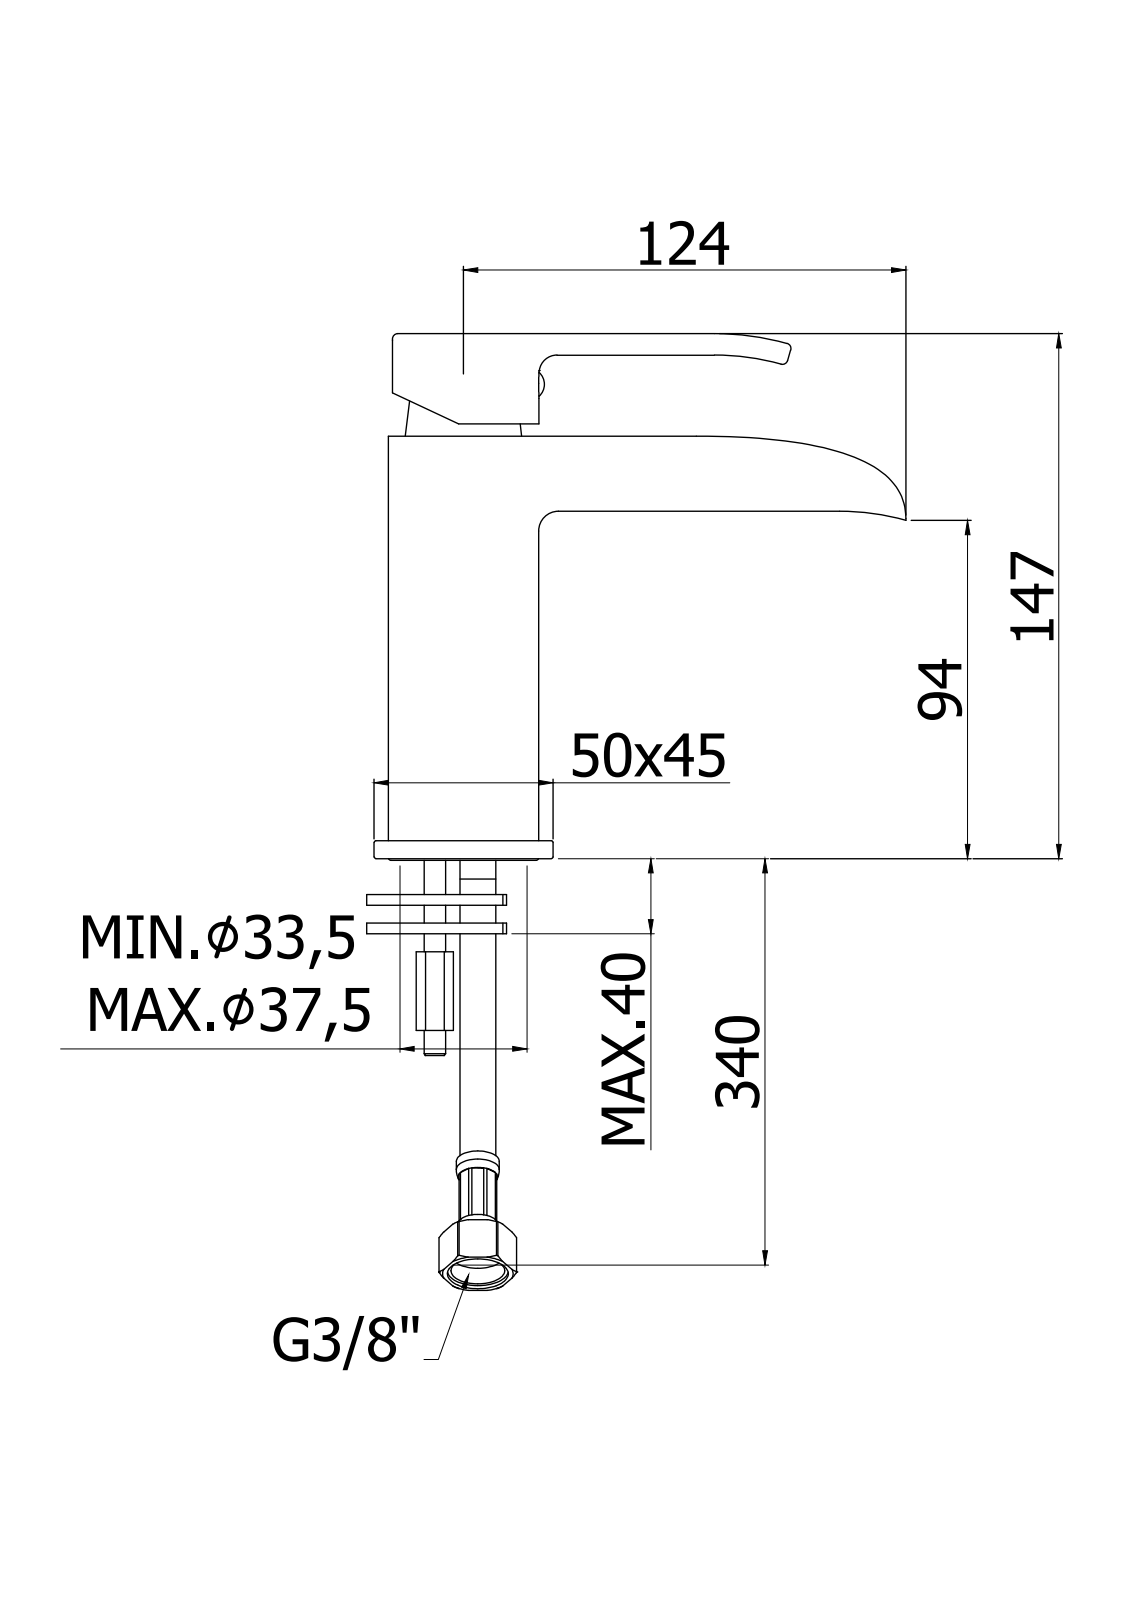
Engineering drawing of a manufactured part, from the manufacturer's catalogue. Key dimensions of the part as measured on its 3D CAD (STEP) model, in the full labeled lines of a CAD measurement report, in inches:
Part name (STEP PRODUCT): LES061CR
STEP written by: CREO PARAMETRIC BY PTC INC, 2020044 (CONFIG_CONTROL_DESIGN)
Units: inches
Bodies: 1 solid, 1145 faces (337 planar, 435 cylindrical, 373 other)
Overall size (bounding box): 5.865 × 5.737 × 1.772
Volume: 9.226 in³ · Surface area: 142.2 in²
Round holes (diameter × count): ⌀0.098 ×6, ⌀0.197 ×5, ⌀0.217 ×4, ⌀0.244 ×2, ⌀0.276 ×2, ⌀0.339 ×2, ⌀0.37 ×2, ⌀0.118 ×1, ⌀0.307 ×1, ⌀0.657 ×1, ⌀0.756 ×1, ⌀0.795 ×1
Round bosses / shafts (diameter × count): ⌀0.157 ×2, ⌀1.528 ×1, ⌀1.26 ×1, ⌀1.24 ×1, ⌀1.161 ×1, ⌀1.102 ×1, ⌀1.004 ×1, ⌀0.984 ×1
Partial cylindrical surfaces — rounded edges, fillets, slot ends (radius × count): R0.02 ×59, R0.059 ×48, R0.079 ×18, R0.039 ×14, R0.028 ×10, R0.031 ×6, R0.157 ×6, R0.01 ×4
Main face-to-face distances: 1.457, 0.02, 0.098, 0.118, 1.339, 0.128, 1.526, 1.358, 1.24, 0.039
Hole centre spacings: 0.512, 0.265, 0.415, 0.431, 0.03, 0.22, 0.247, 0.268
